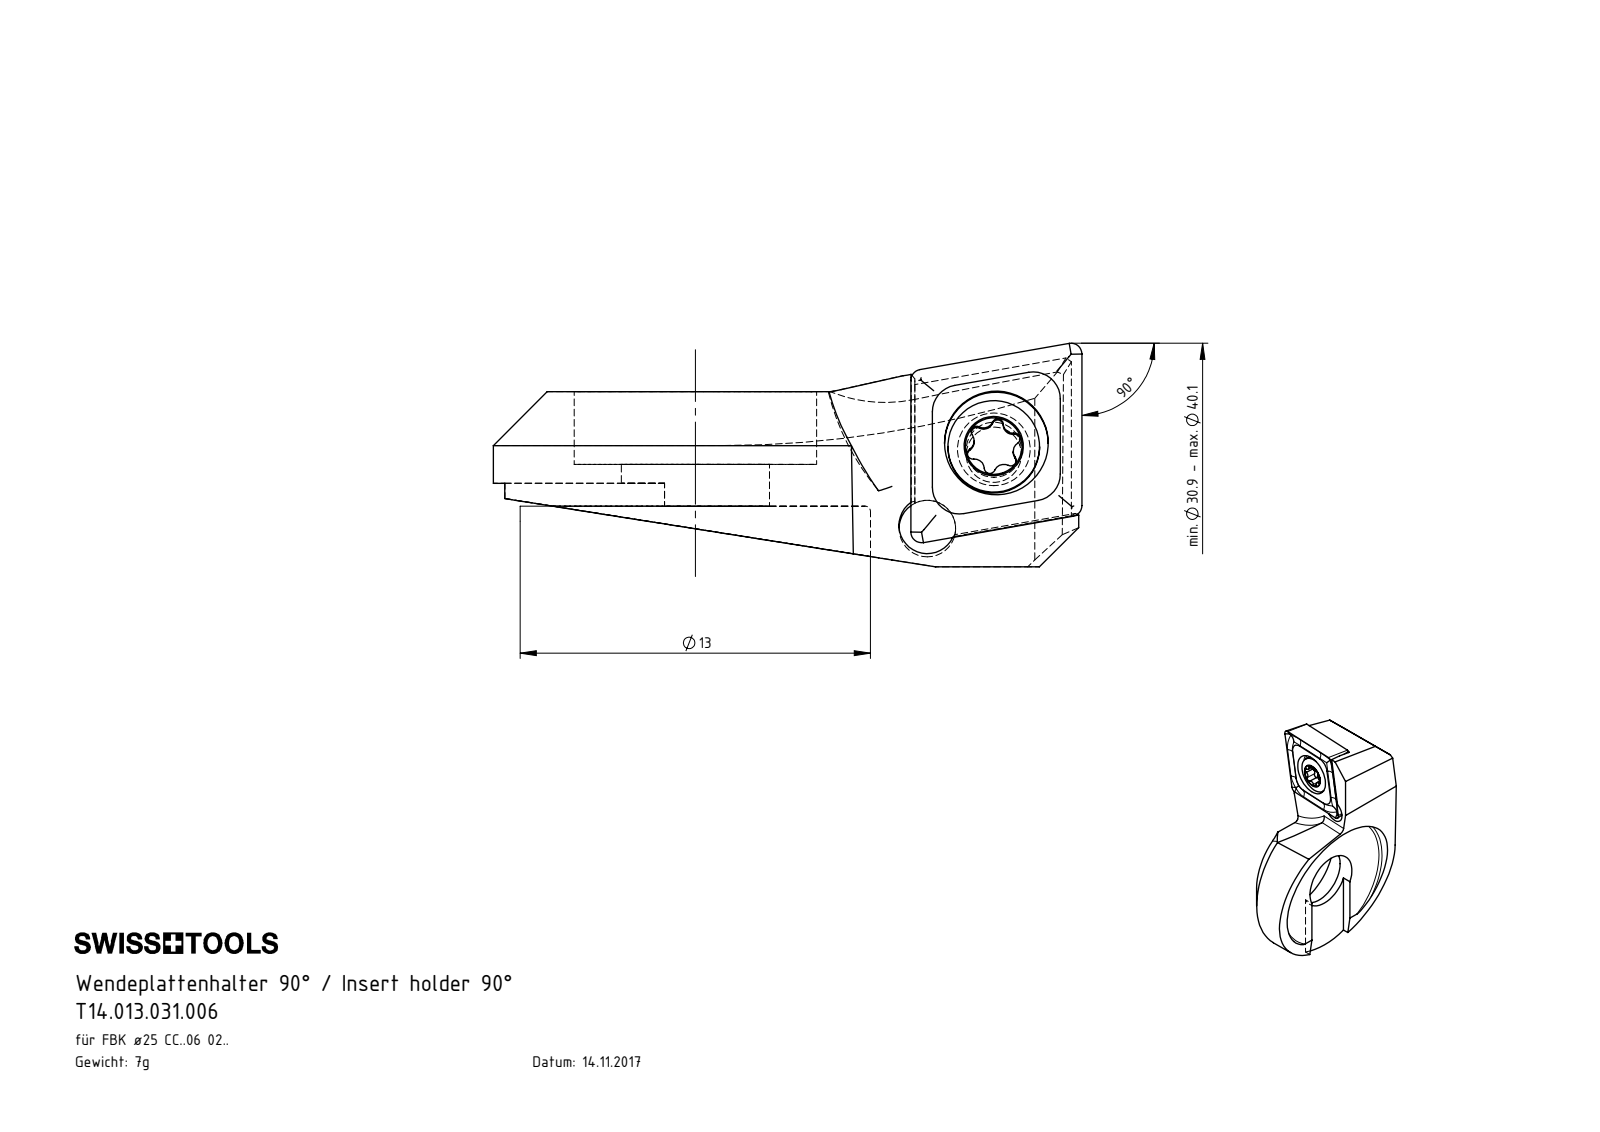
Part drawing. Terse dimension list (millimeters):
name: F25-WCA.001.006_D_fertigbearbeitet; F25.WCA.001.006; CCMT060204; WCA-ER2.001.006_A
written by: SolidWorks 2017 (AUTOMOTIVE_DESIGN)
unit: mm
bodies: 3 solids, 103 faces (39 planar, 26 cylindrical, 38 other)
size: 21.85 × 15 × 8.3
volume: 783 mm³; area: 1 050 mm²
holes: 1× ⌀2.05, 1× ⌀2.1, 1× ⌀2.8, 1× ⌀3.85, 1× ⌀5.5, 1× ⌀9
bosses: 1× ⌀3.4, 1× ⌀2.5
rounds: 6× R0.21, 5× R0.36, 2× R0.5, 1× R0.36, 1× R6.4, 1× R6.5, 1× R7.5, 1× R9
face distances: 1.55, 2.7, 4.25, 3.4, 0.7, 0.85, 6.5, 3.8, 3.1, 2.25
hole spacings: 3.84, 3.99
